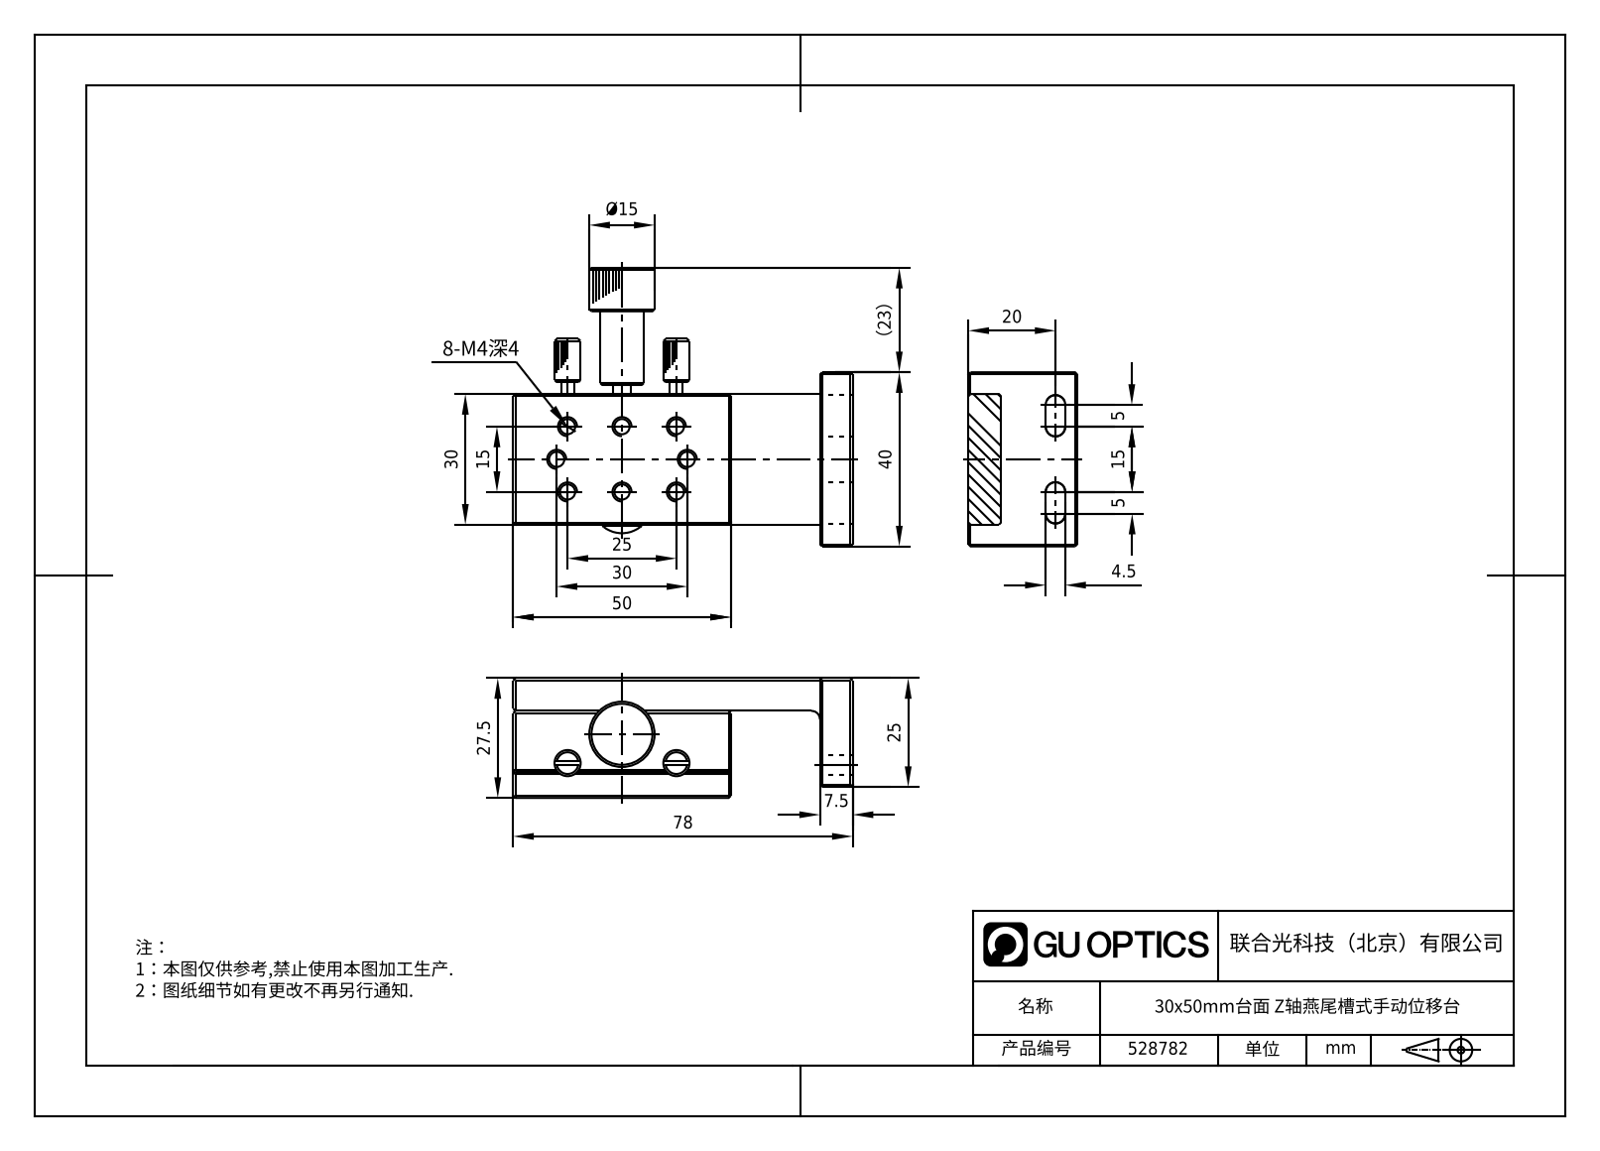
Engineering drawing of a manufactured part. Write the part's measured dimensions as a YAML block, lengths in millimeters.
part_name: "528782"
step_written_by: "SolidWorks 2020 (CONFIG_CONTROL_DESIGN)"
units: millimeters
bodies: {solids: 18, faces: 775, planar: 484, cylindrical: 145, other: 146}
overall_size: [78, 62, 27.5]
volume: 53540
surface_area: 29528
round_holes:
  - {diameter: 2.5, count: 9}
  - {diameter: 3.3, count: 8}
  - {diameter: 4.5, count: 7}
  - {diameter: 8, count: 5}
  - {diameter: 1.6, count: 2}
  - {diameter: 2.05, count: 2}
  - {diameter: 2.4, count: 2}
  - {diameter: 3.4, count: 2}
  - {diameter: 6, count: 2}
  - {diameter: 7.7, count: 2}
  - {diameter: 4, count: 1}
  - {diameter: 4.1, count: 1}
round_bosses_or_shafts:
  - {diameter: 7, count: 6}
  - {diameter: 9, count: 4}
  - {diameter: 4, count: 4}
  - {diameter: 5.5, count: 2}
  - {diameter: 3, count: 2}
  - {diameter: 2.95, count: 2}
  - {diameter: 2.6, count: 2}
  - {diameter: 8, count: 1}
partial_cylinders:
  - {radius: 2.25, count: 4}
  - {radius: 1.55, count: 2}
  - {radius: 7.5, count: 1}
face_to_face_distances: [7.5, 21.5, 14, 6, 30, 20, 27.5, 6.5, 3.9, 3.8]
hole_center_spacings: [15, 7.91, 8, 9.01, 10.61, 12.5, 12.9, 14.5]
